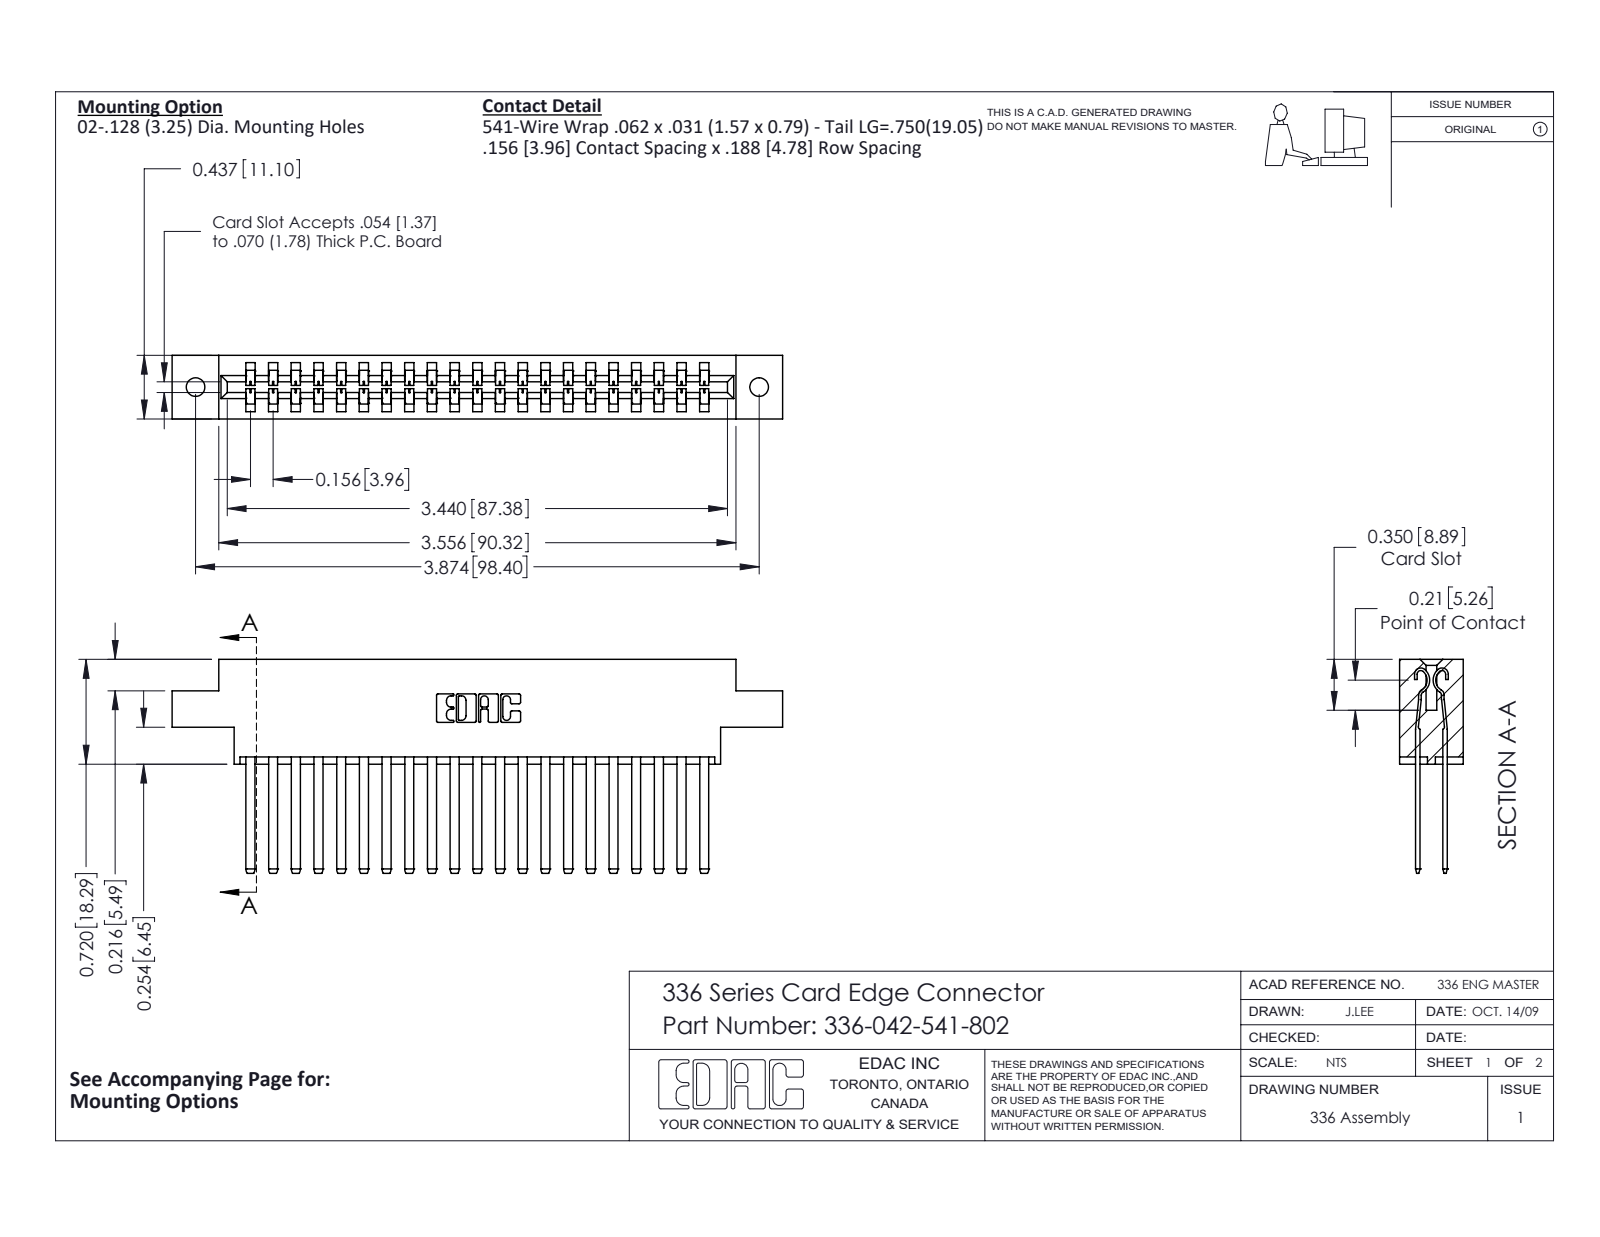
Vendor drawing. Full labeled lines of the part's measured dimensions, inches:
Part name (STEP PRODUCT): 336-290-001_336-290-541; 336 Part_Offset - .128 Dia; 336-042-541-802
STEP written by: SolidWorks 2020 (CONFIG_CONTROL_DESIGN)
Units: inches
Bodies: 43 solids, 1882 faces (1166 planar, 716 cylindrical, 0 other)
Overall size (bounding box): 4.197 × 1.47 × 0.437
Volume: 0.952 in³ · Surface area: 30.16 in²
Round holes (diameter × count): ⌀0.128 ×2
Partial cylindrical surfaces — rounded edges, fillets, slot ends (radius × count): R0.004 ×84, R0.056 ×42, R0.01 ×22, R0.007 ×6, R0.031 ×6, R0.022 ×4, R0.04 ×4, R0.026 ×3
Main face-to-face distances: 0.188, 0.328, 0.14, 0.297, 0.109, 0.031, 0.437, 0.033, 0.156, 0.181
Hole centre spacings: 3.874
